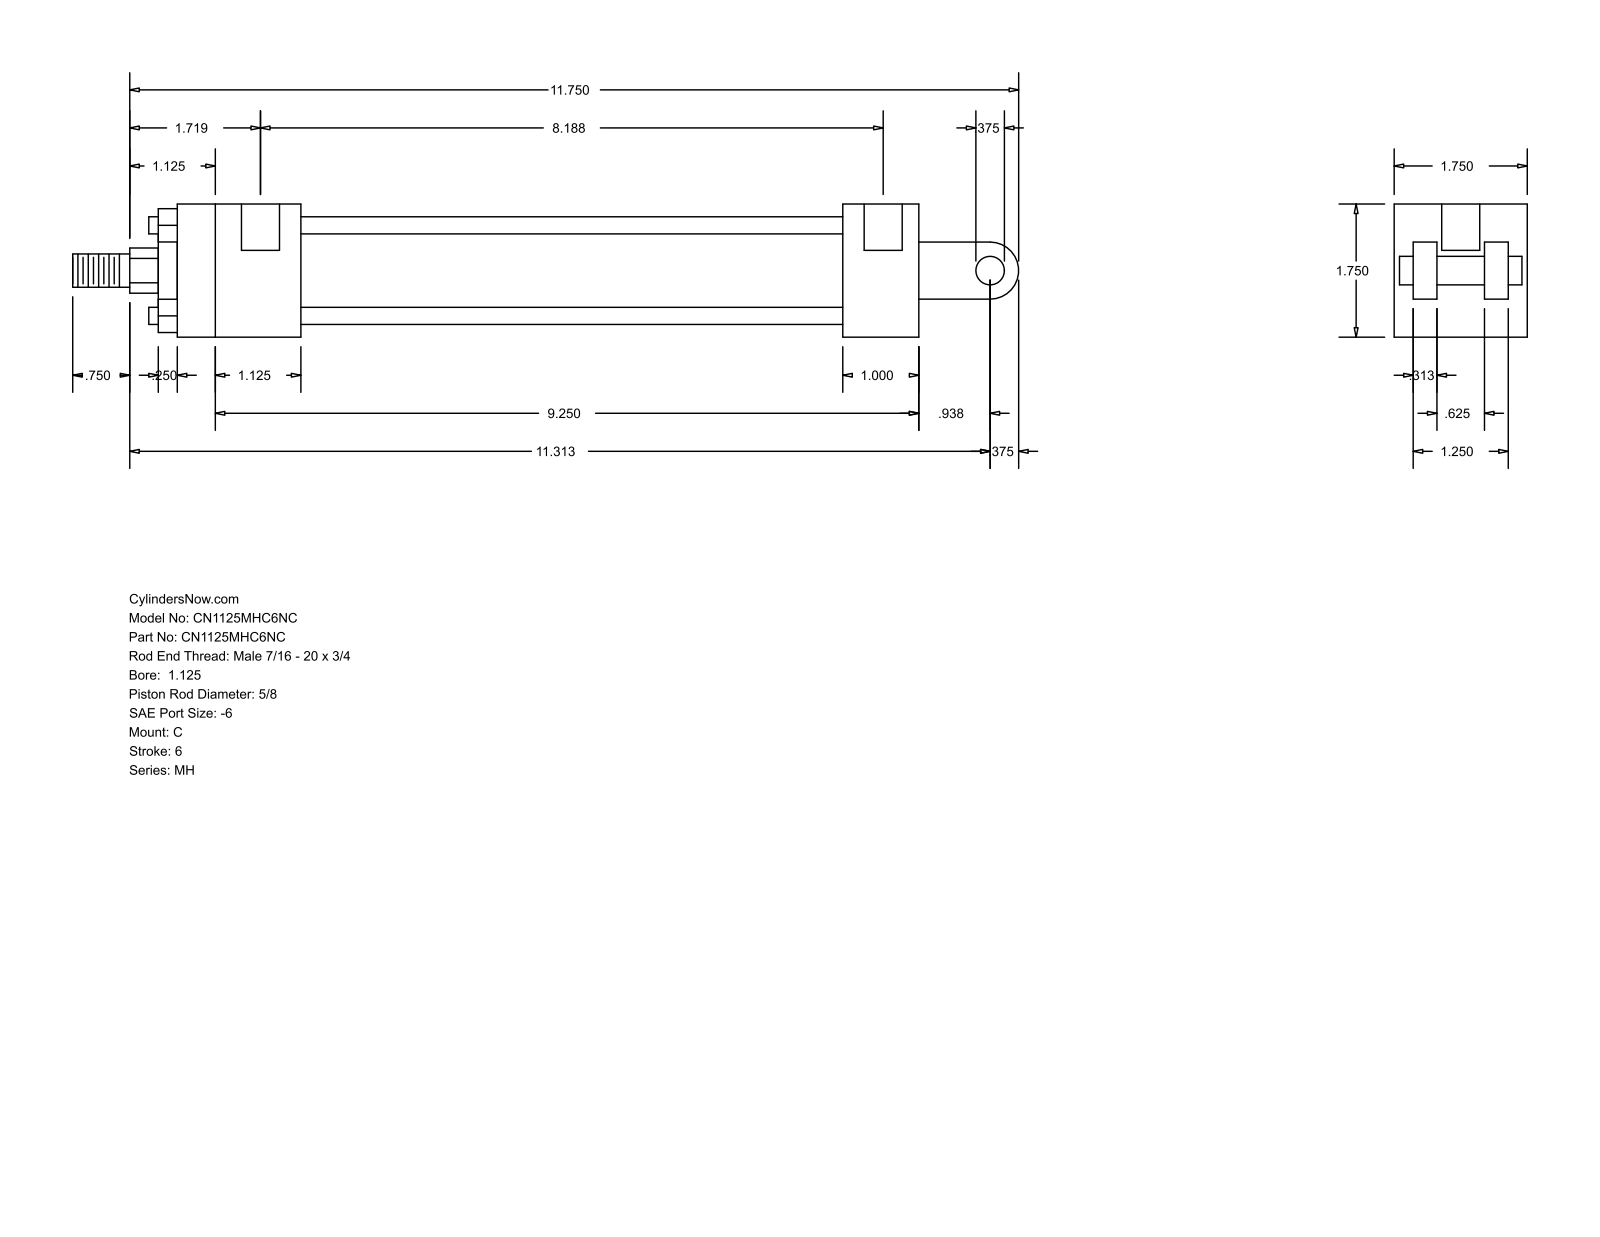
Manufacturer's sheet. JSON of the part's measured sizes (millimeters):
{"part_name": "MH_C__0112_0.625", "step_written_by": "GSSL Pune (CONFIG_CONTROL_DESIGN)", "units": "millimeters", "bodies": {"solids": 0, "faces": 99, "planar": 70, "cylindrical": 29, "other": 0}, "overall_size": [315.91, 44.45, 44.45], "round_holes": [[5.56, 4], [12.7, 2]], "round_bosses_or_shafts": [[5.71, 4], [34.92, 1], [28.57, 1], [15.88, 1], [11.11, 1], [9.53, 1]], "partial_cylinders_radius": [[7.54, 1], [9.53, 1]], "face_to_face_distances": [44.46, 6.35, 31.76, 14.29, 25.4, 30.17, 38.11, 7.94, 23.82, 41.27], "hole_center_spacings": [204.79, 3.17, 207.96]}
